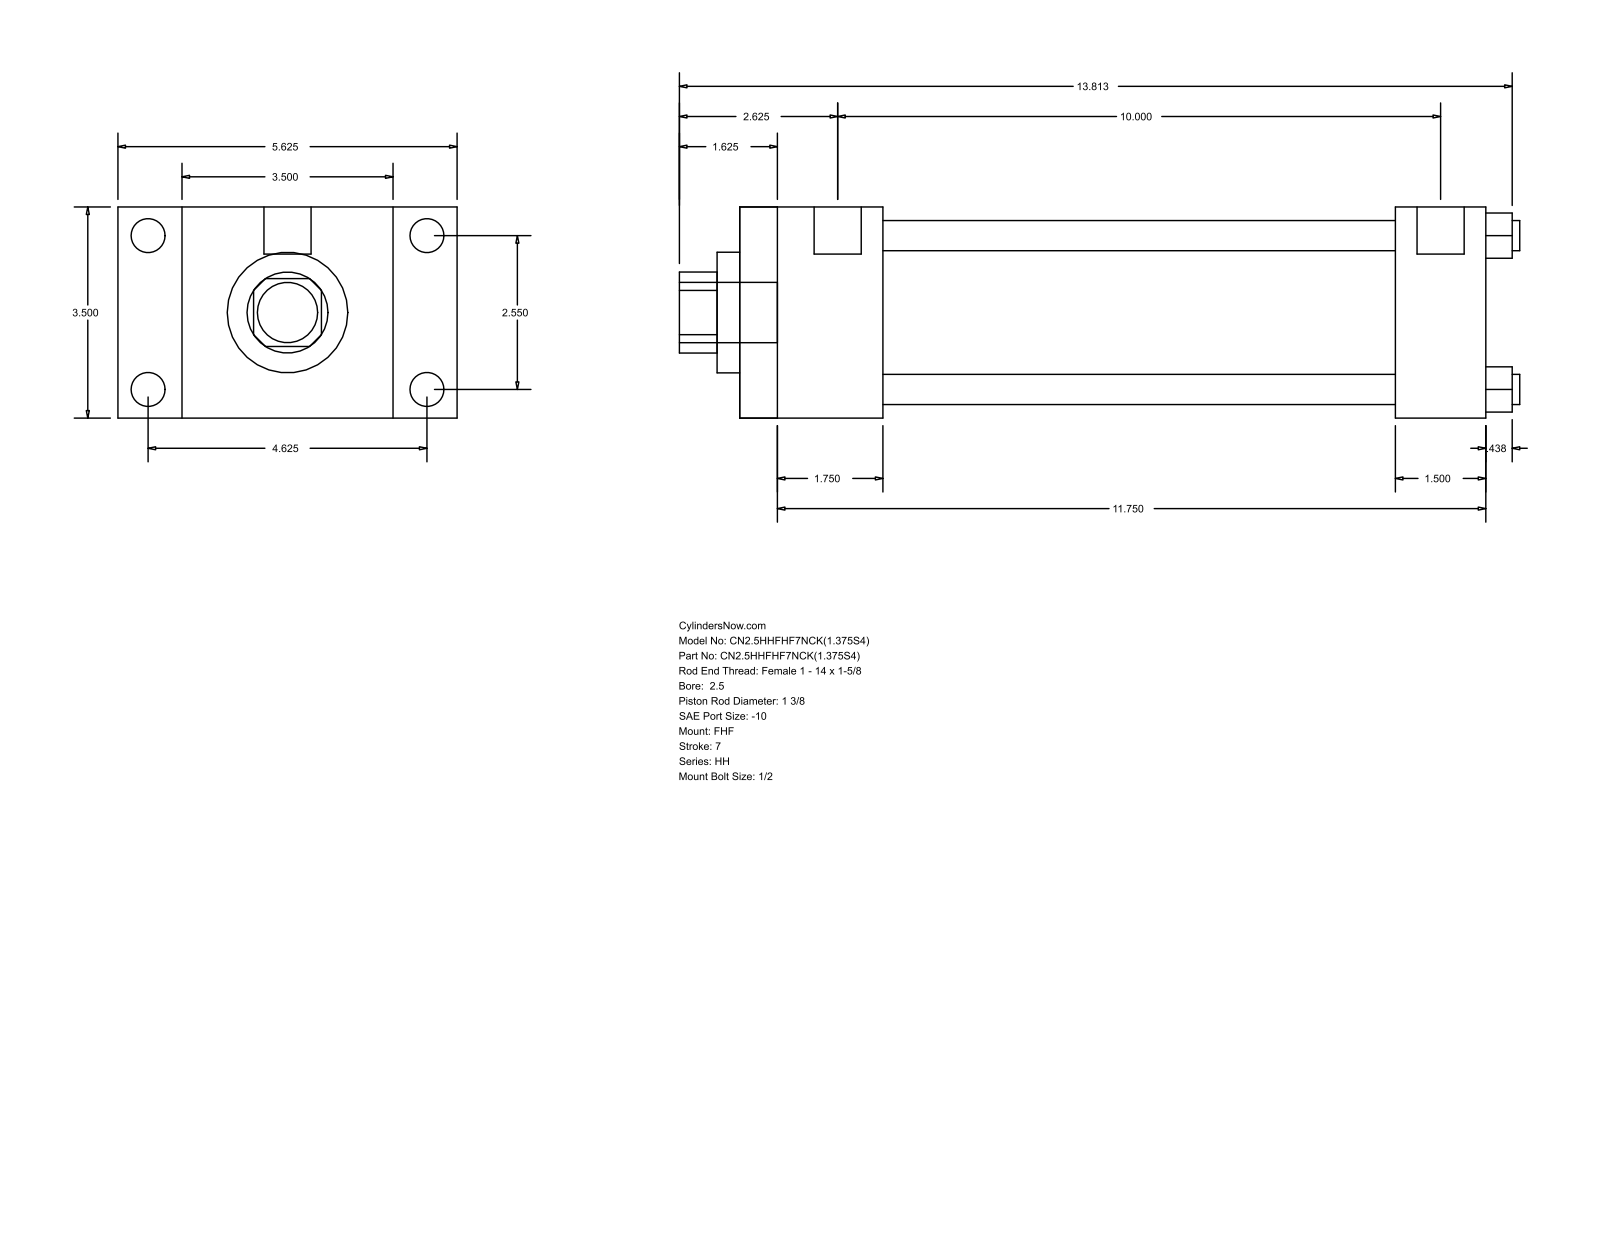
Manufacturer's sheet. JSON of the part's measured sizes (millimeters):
{"part_name": "HH_FHF__0250_1.375", "step_written_by": "GSSL Pune (CONFIG_CONTROL_DESIGN)", "units": "millimeters", "bodies": {"solids": 0, "faces": 88, "planar": 60, "cylindrical": 28, "other": 0}, "overall_size": [354.01, 142.88, 88.9], "round_holes": [[12.7, 4], [34.92, 1], [50.8, 1], [73.03, 1]], "round_bosses_or_shafts": [[14.3, 4], [5.56, 4], [19.84, 2], [25.4, 1]], "partial_cylinders_radius": [[17.06, 1]], "face_to_face_distances": [88.9, 60.32, 26.99, 115.89, 314.33, 254.01, 142.88, 276.22, 215.9, 38.11], "hole_center_spacings": [45.79, 64.76, 91.58]}
